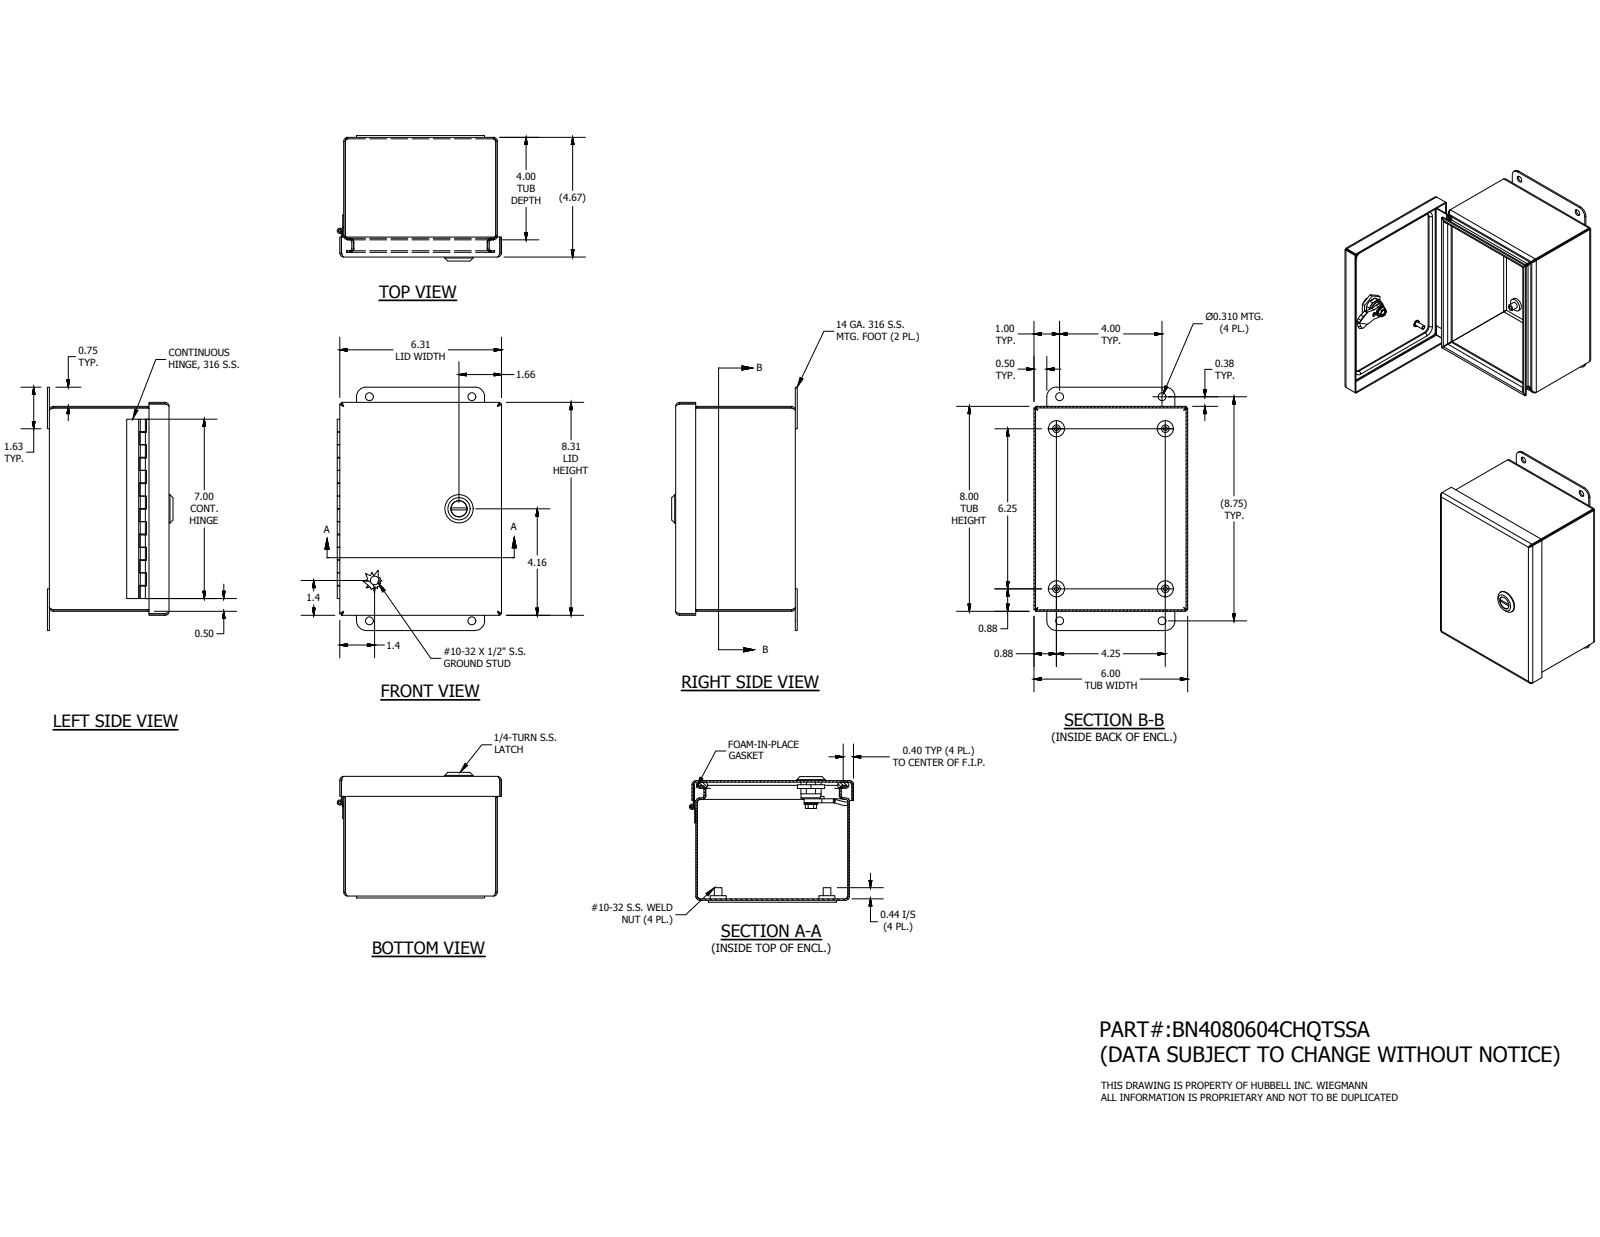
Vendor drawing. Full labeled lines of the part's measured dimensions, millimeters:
Part name (STEP PRODUCT): BN40806CHQTSSALID; 8x6; 348128; 328145LH (+8 more)
STEP written by: Autodesk Inventor 2016 (AUTOMOTIVE_DESIGN)
Units: millimetres
Bodies: 21 solids, 631 faces (342 planar, 192 cylindrical, 97 other)
Overall size (bounding box): 241.3 × 162.86 × 124.59
Volume: 323 598 mm³ · Surface area: 396 861 mm²
Round holes (diameter × count): ⌀3.96 ×4, ⌀7.87 ×4, ⌀2.96 ×1, ⌀5 ×1, ⌀8 ×1, ⌀10 ×1, ⌀10.2 ×1, ⌀16.1 ×1, ⌀20.38 ×1
Round bosses / shafts (diameter × count): ⌀15.88 ×4, ⌀7.62 ×4, ⌀28 ×1, ⌀19.8 ×1, ⌀16 ×1, ⌀15.2 ×1, ⌀13.5 ×1, ⌀12.8 ×1
Partial cylindrical surfaces — rounded edges, fillets, slot ends (radius × count): R2.38 ×20, R3.88 ×20, R3.17 ×16, R0.5 ×8, R4 ×4, R9.53 ×4, R2.31 ×2, R6.45 ×1
Main face-to-face distances: 1.5, 1.49, 117.19, 118.68, 115.69, 117.18, 201.7, 150.91, 152.4, 149.41
Hole centre spacings: 31.91, 109.48, 190.53, 217.41, 101.6, 107.95, 158.75, 191.98
